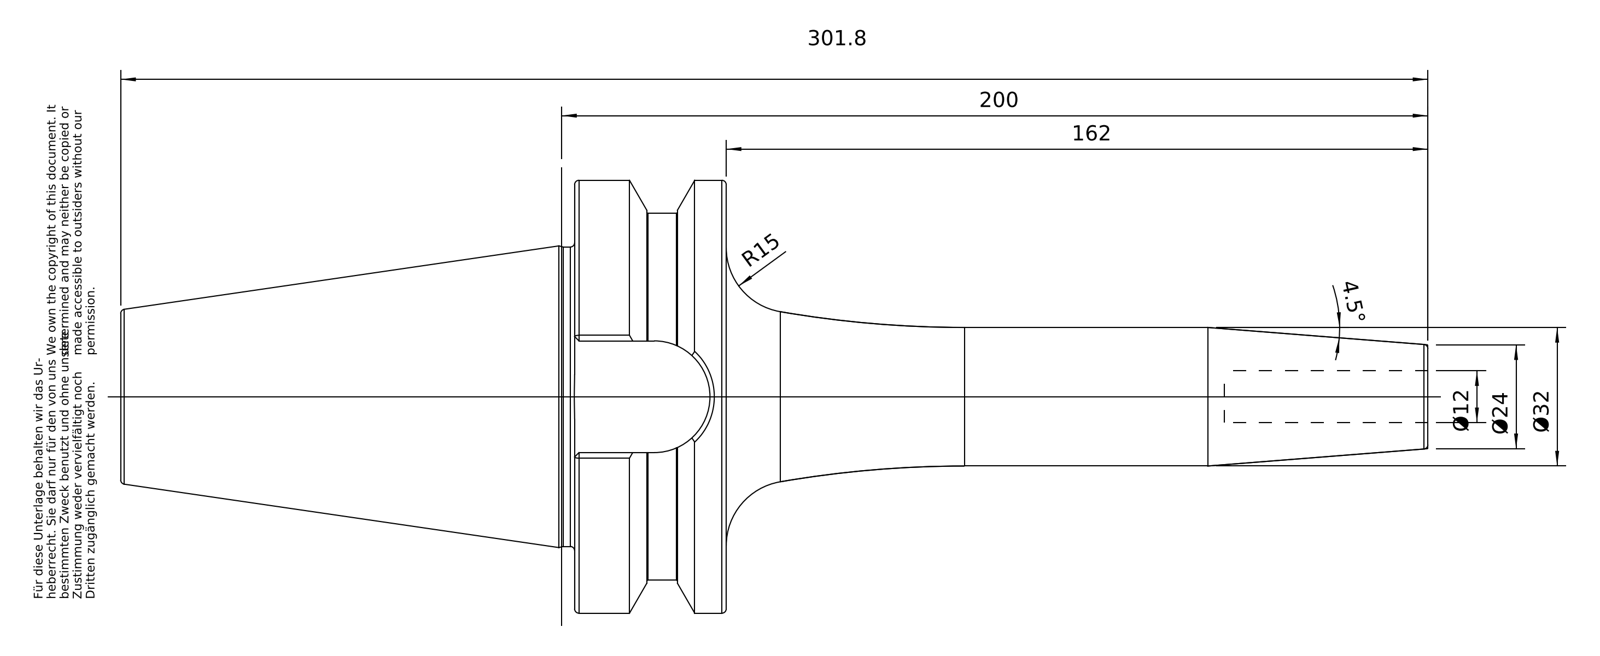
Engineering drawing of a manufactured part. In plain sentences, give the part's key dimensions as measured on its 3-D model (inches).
The part is named "50-646-12". Its 3-D file was written by "PRO/ENGINEER BY PARAMETRIC TECHNOLOGY CORPORATION, 2010430 (CONFIG_CONTROL_DESIGN)". It is 1 solid with 98 faces: 26 planar, 22 cylindrical and 50 other. Overall it measures 11.882 by 3.936 by 3.936 inches. Its volume is 36.66 cubic inches and its surface area 106.1 square inches. Round holes: 1 of diameter 0.472, 1 of diameter 0.817, 1 of diameter 0.985, 1 of diameter 1.012. Round bosses or shafts: 1 of diameter 3.936, 1 of diameter 3.337, 1 of diameter 2.722, 1 of diameter 1.26, 1 of diameter 0.945. Partial cylindrical surfaces (rounded edges, fillets, slot ends): 1 of radius 0.508. The main face-to-face distances are 1.378, 2.772, 4.126, 5.504, 1.016, 11.882, 7.756, 6.378, 1.89, 2.236.
